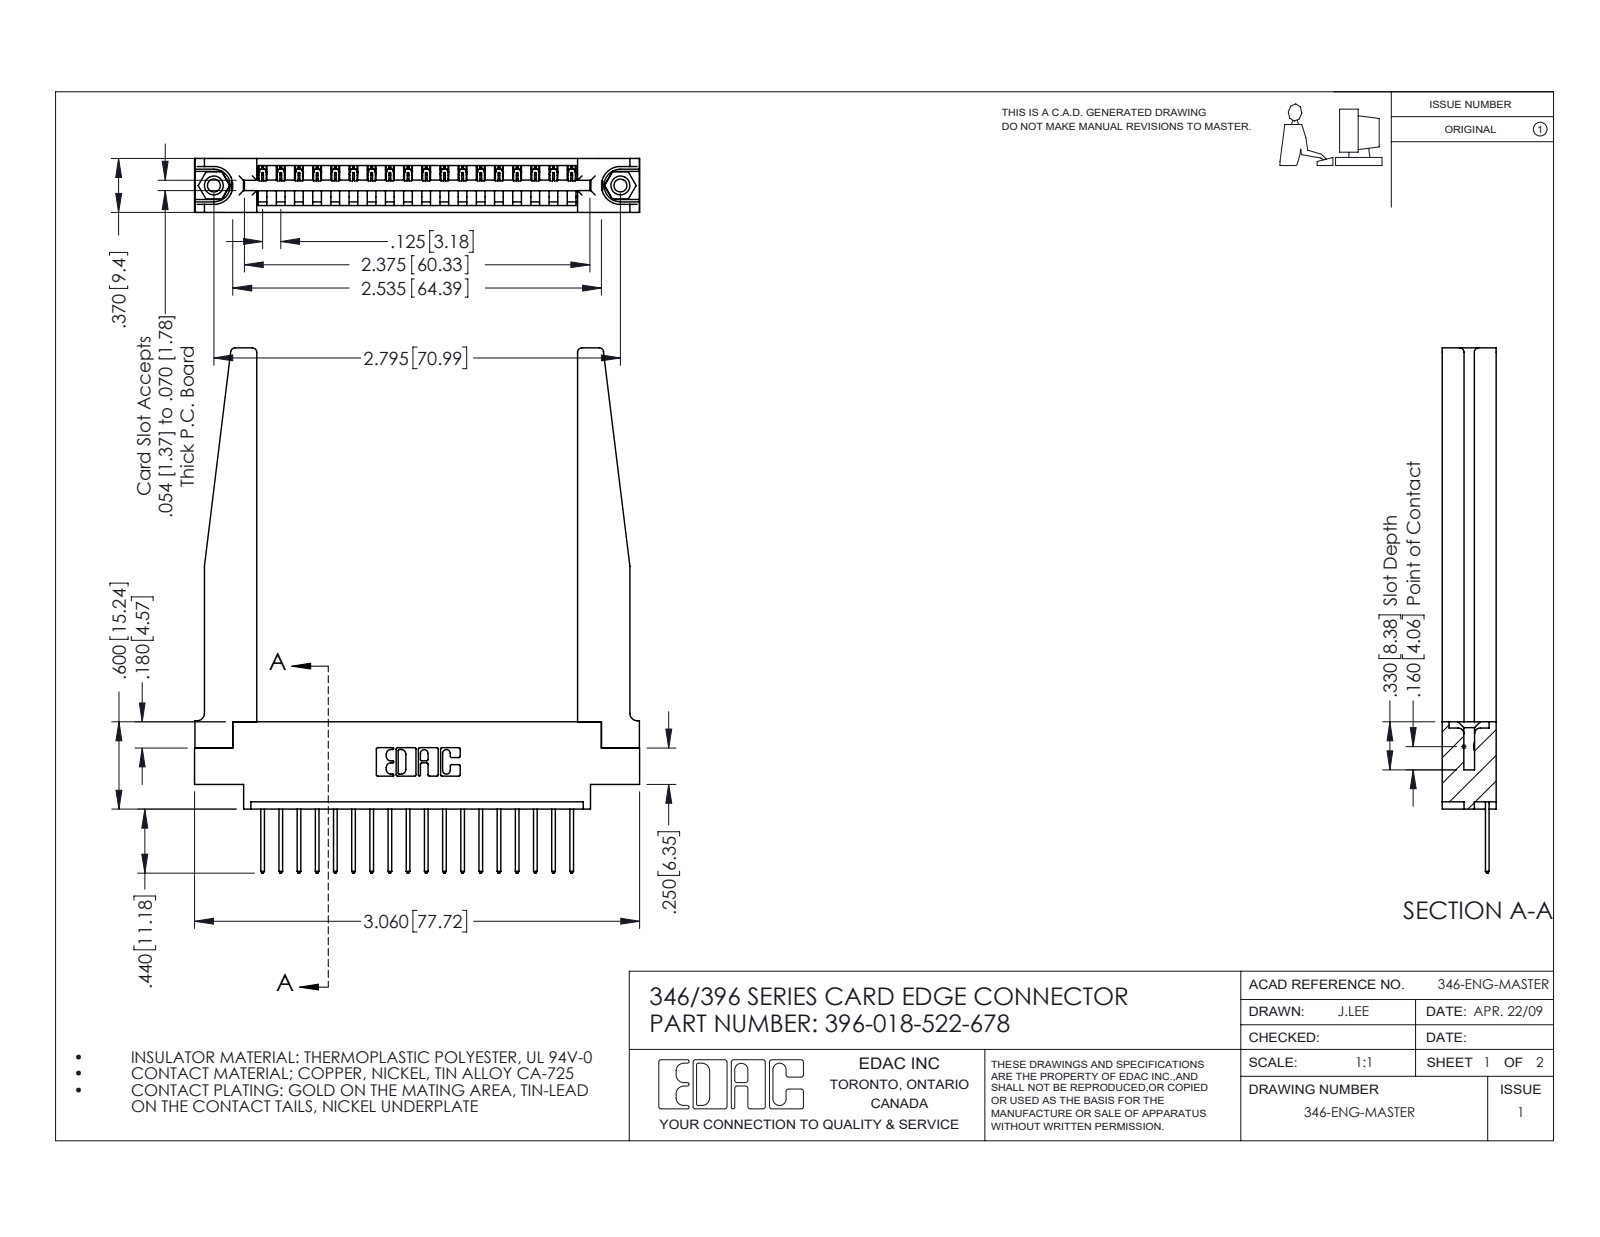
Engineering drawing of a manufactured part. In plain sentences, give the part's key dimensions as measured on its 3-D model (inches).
The part is named "345-250-001_345-250-001-102; 346-220-078_345-220-078; 396-018-522-678; 345-292-001_345-293-122 (+1 more)". Its 3-D file was written by "SolidWorks 2016 (CONFIG_CONTROL_DESIGN)". It is 23 solids with 1404 faces: 942 planar, 410 cylindrical and 52 other. Overall it measures 3.61 by 3.06 by 0.37 inches. Its volume is 0.856 cubic inches and its surface area 23.88 square inches. Round holes: 2 of diameter 0.089, 2 of diameter 0.125, 2 of diameter 0.156, 1 of diameter 0.064. Round bosses or shafts: 2 of diameter 0.155. Partial cylindrical surfaces (rounded edges, fillets, slot ends): 36 of radius 0.006, 36 of radius 0.01, 22 of radius 0.01, 8 of radius 0.03, 6 of radius 0.007, 6 of radius 0.031, 3 of radius 0.026, 2 of radius 0.031. The main face-to-face distances are 0.37, 0.072, 0.048, 0.322, 0.15, 0.148, 0.25, 0.298, 0.025, 0.102. The hole center spacings are 0.246, 2.588, 2.795.
